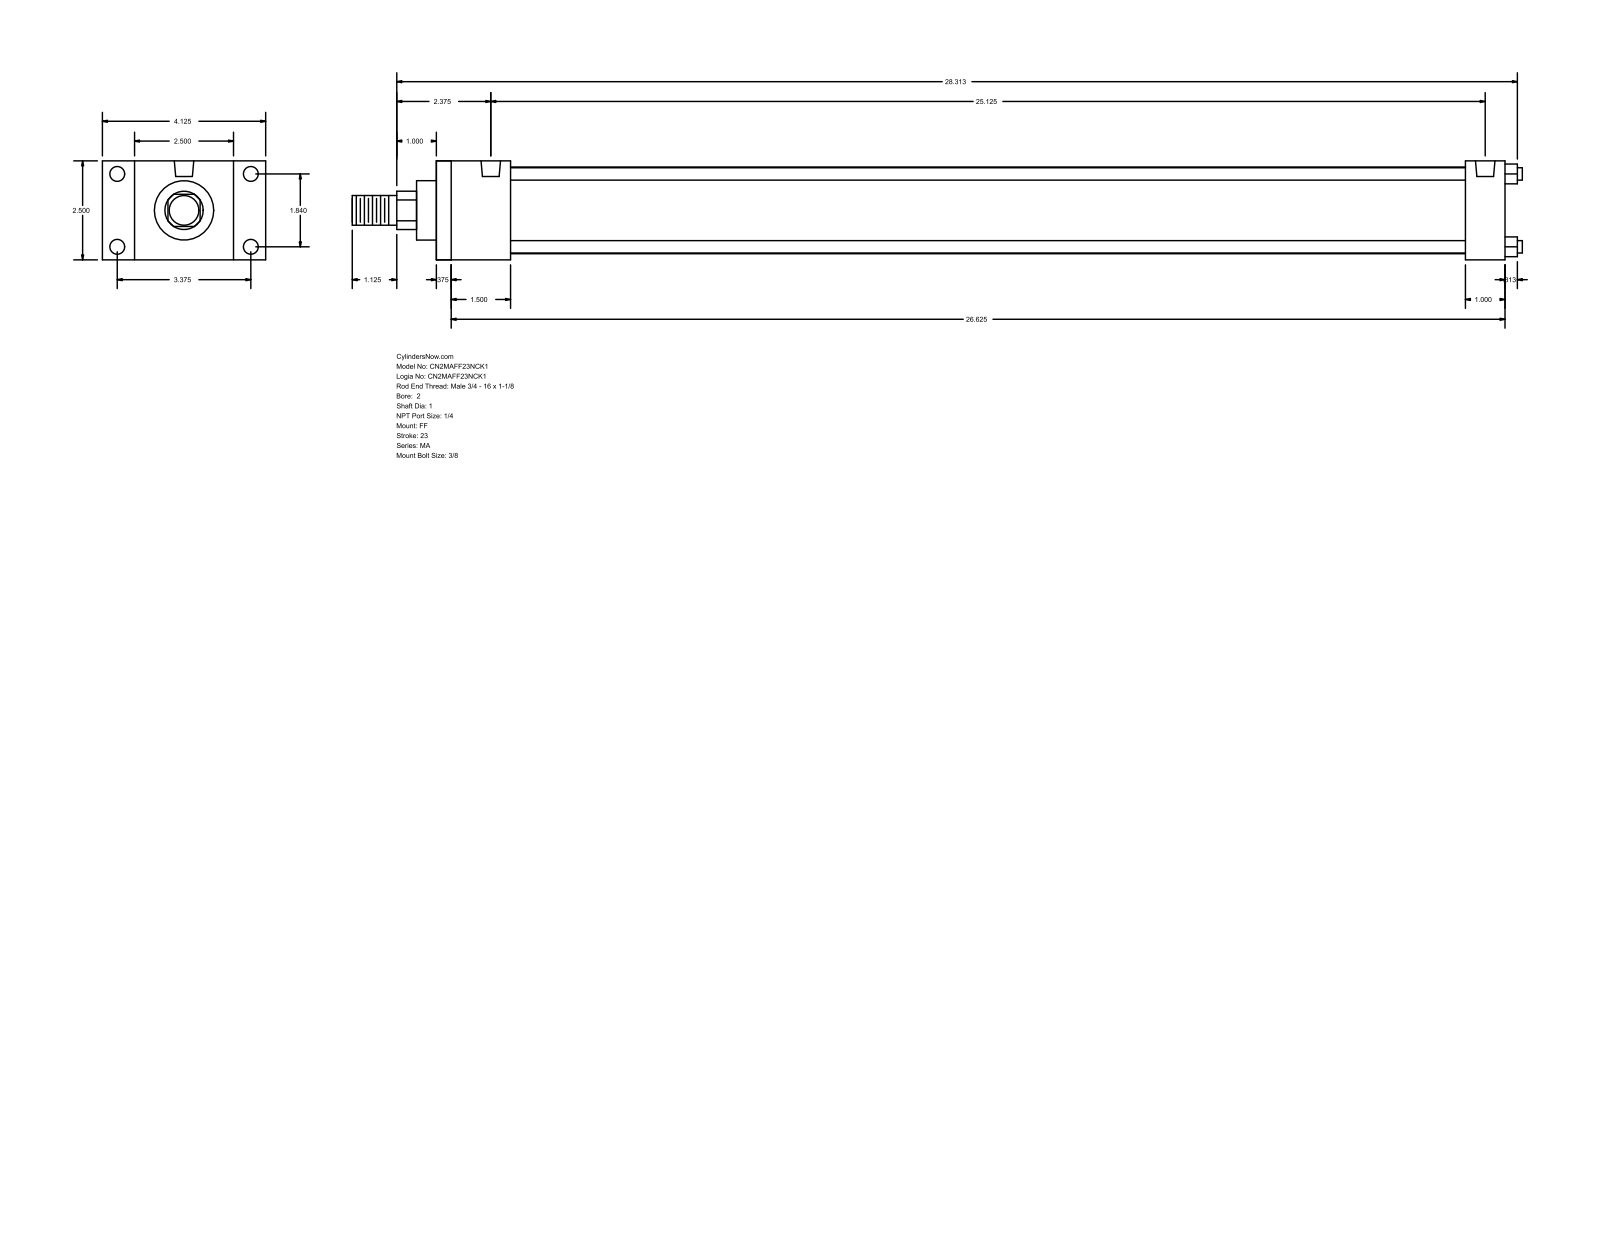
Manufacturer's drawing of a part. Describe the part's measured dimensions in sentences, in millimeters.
The part is named "MA_FF__0200_1". Its 3-D file was written by "GSSL Pune (CONFIG_CONTROL_DESIGN)". It is 0 solids with 92 faces: 64 planar, 28 cylindrical and 0 other. Overall it measures 750.89 by 104.78 by 63.5 millimeters. Round holes: 4 of diameter 7.94, 4 of diameter 9.53, 2 of diameter 12.49. Round bosses or shafts: 4 of diameter 7.94, 1 of diameter 55.63, 1 of diameter 38.1, 1 of diameter 25.4, 1 of diameter 19.05. Partial cylindrical surfaces (rounded edges, fillets, slot ends): 1 of radius 12.29. The main face-to-face distances are 63.5, 685.8, 9.52, 676.28, 25.4, 20.64, 12.7, 47.63, 660.4, 38.11. The hole center spacings are 46.74, 85.72, 97.63, 638.17.
